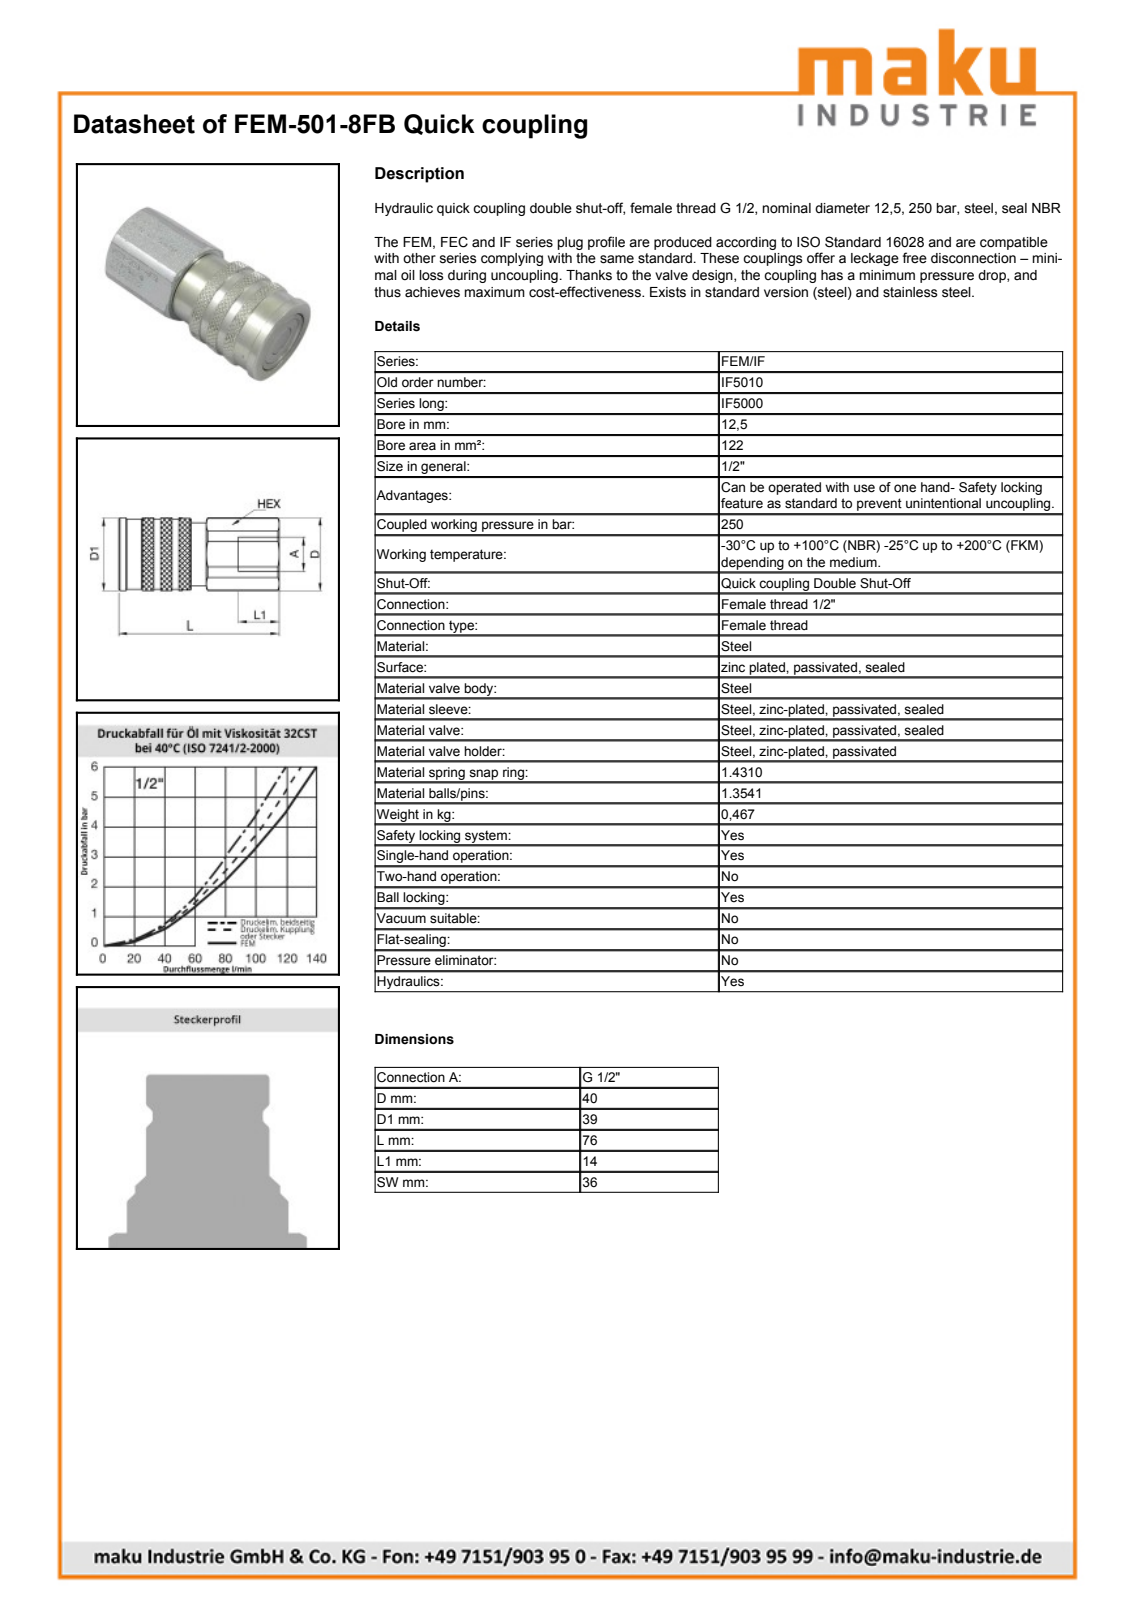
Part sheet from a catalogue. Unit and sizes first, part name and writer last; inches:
Units: inches
Overall size (bounding box): 2.988 × 1.575 × 1.496
Round holes (diameter × count): ⌀0.62 ×1, ⌀0.733 ×1, ⌀0.972 ×1, ⌀1.209 ×1, ⌀1.354 ×1
Round bosses / shafts (diameter × count): ⌀1.496 ×1, ⌀1.445 ×1, ⌀1.346 ×1, ⌀1.339 ×1, ⌀1.263 ×1, ⌀1.181 ×1, ⌀0.965 ×1, ⌀0.611 ×1
Partial cylindrical surfaces — rounded edges, fillets, slot ends (radius × count): R0.02 ×2, R0.787 ×1
Main face-to-face distances: 1.417, 2.988, 2.976, 0.635, 2.341, 2.353, 1.26, 0.625, 1.717, 1.728
Volume: 4.665 in³ · Surface area: 23.35 in²
Bodies: 2 solids, 134 faces (34 planar, 58 cylindrical, 42 other)
Part name (STEP PRODUCT): FEM-501-8FB
STEP written by: SolidWorks 2009 (AUTOMOTIVE_DESIGN)
